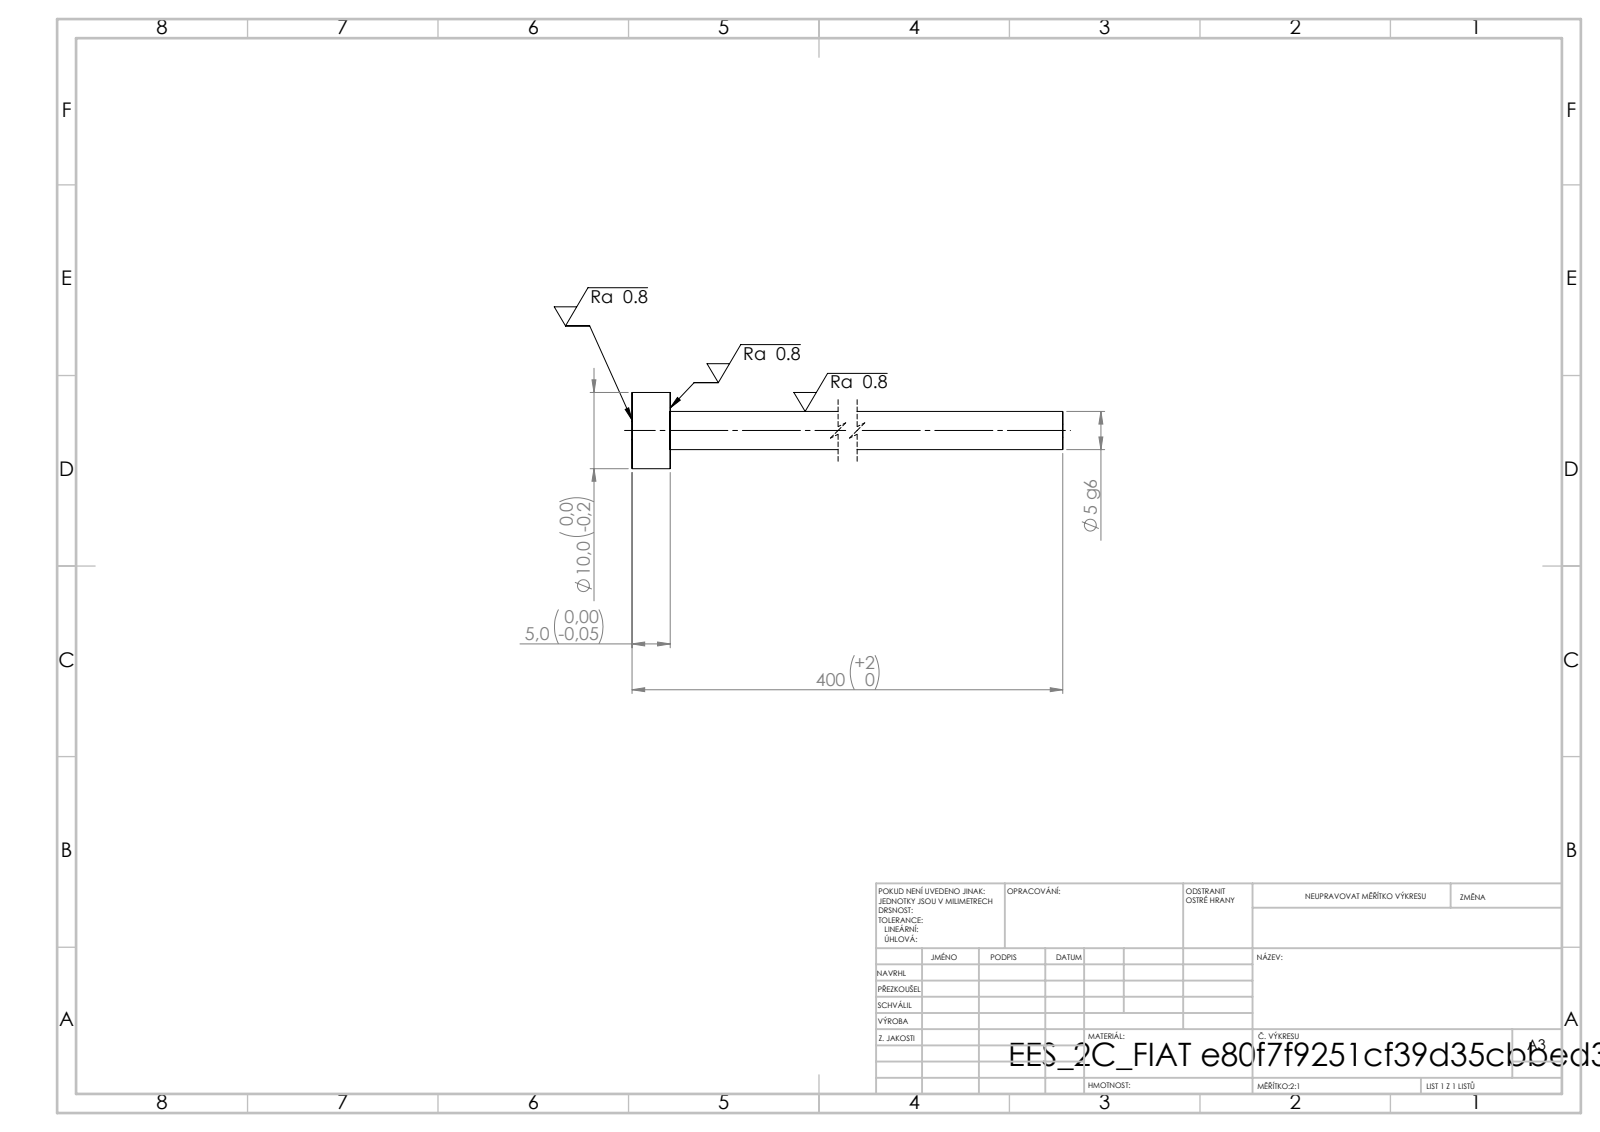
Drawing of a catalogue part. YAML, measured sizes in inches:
step_written_by: "SolidWorks 2019 (CONFIG_CONTROL_DESIGN)"
units: inches
bodies: {solids: 1, faces: 7, planar: 3, cylindrical: 4, other: 0}
overall_size: [15.748, 0.394, 0.394]
volume: 0.497
surface_area: 10.1
round_bosses_or_shafts:
  - {diameter: 0.394, count: 1}
  - {diameter: 0.197, count: 1}
face_to_face_distances: [0.197, 15.748, 15.551]
